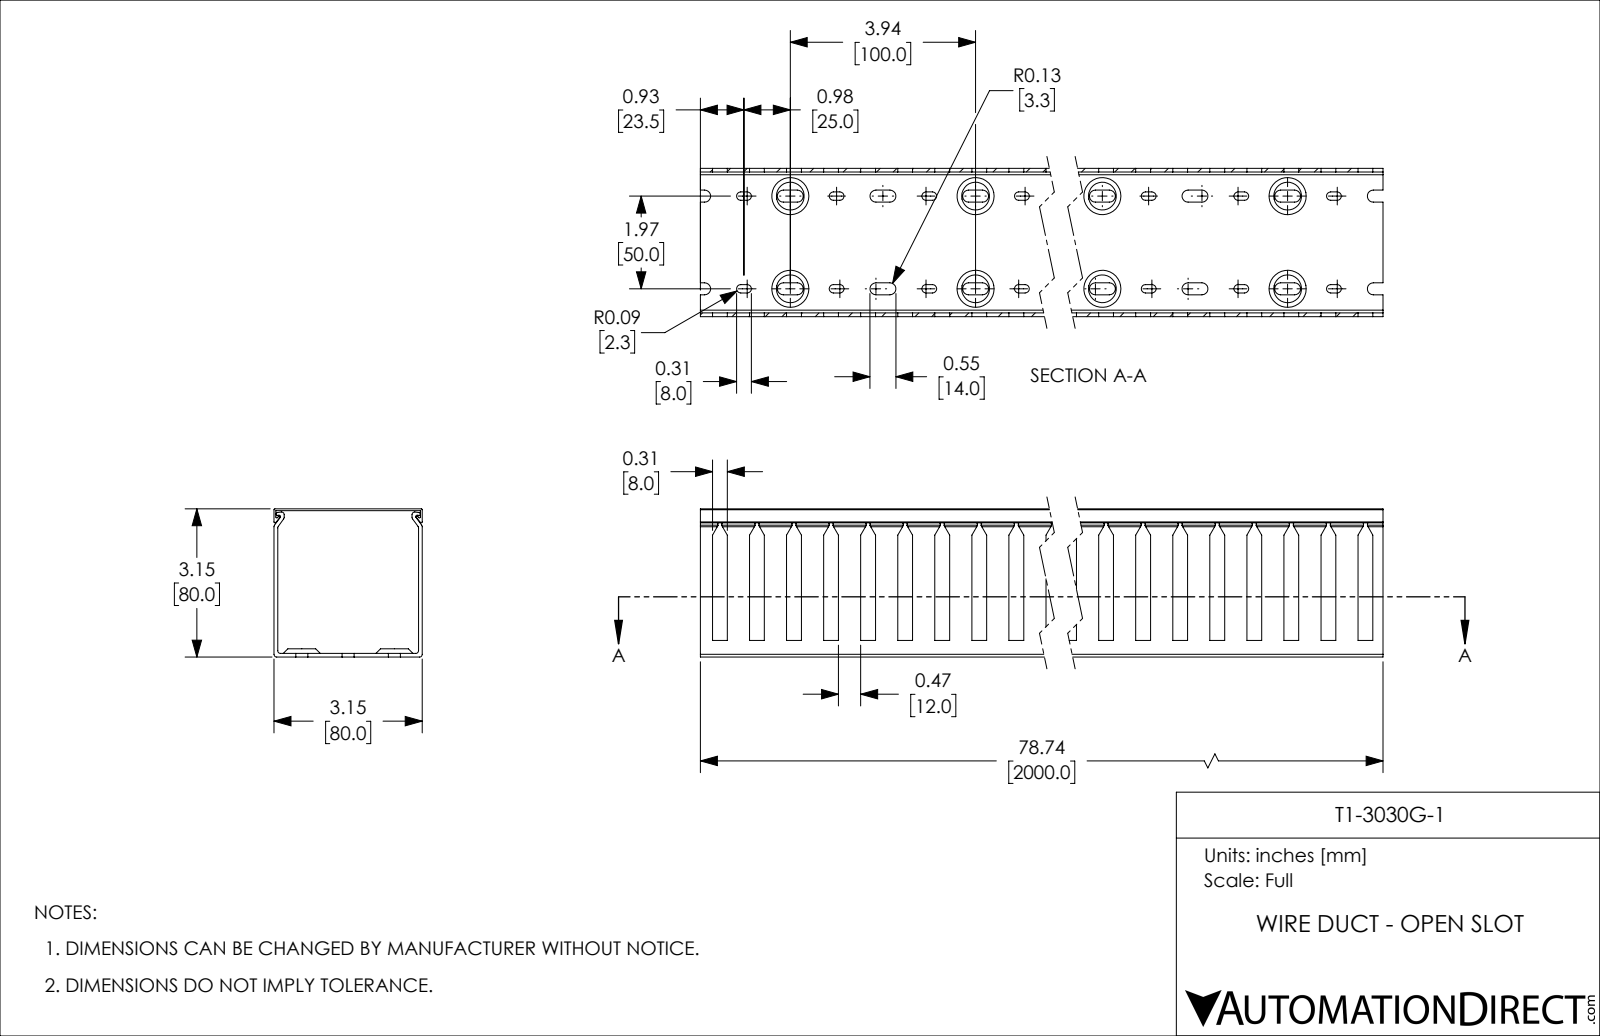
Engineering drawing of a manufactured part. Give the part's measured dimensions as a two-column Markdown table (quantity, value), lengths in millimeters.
| quantity | value |
| --- | --- |
| part name | T1-3030W-1 |
| STEP written by | SolidWorks 2021 (CONFIG_CONTROL_DESIGN) |
| units | millimeters |
| bodies | 2 solids, 1573 faces (762 planar, 731 cylindrical, 80 other) |
| overall size | 2000 × 80 × 80 |
| volume | 1 124 000 mm³ |
| surface area | 1 324 000 mm² |
| partial cylindrical surfaces (radius × count) | 3.25 × 200, 2.25 × 160, 1.5 × 12, 0.5 × 8, 0.75 × 6 |
| main face-to-face distances | 2, 78, 80, 1, 79, 77, 76, 4.5, 74.5, 5.5 |
